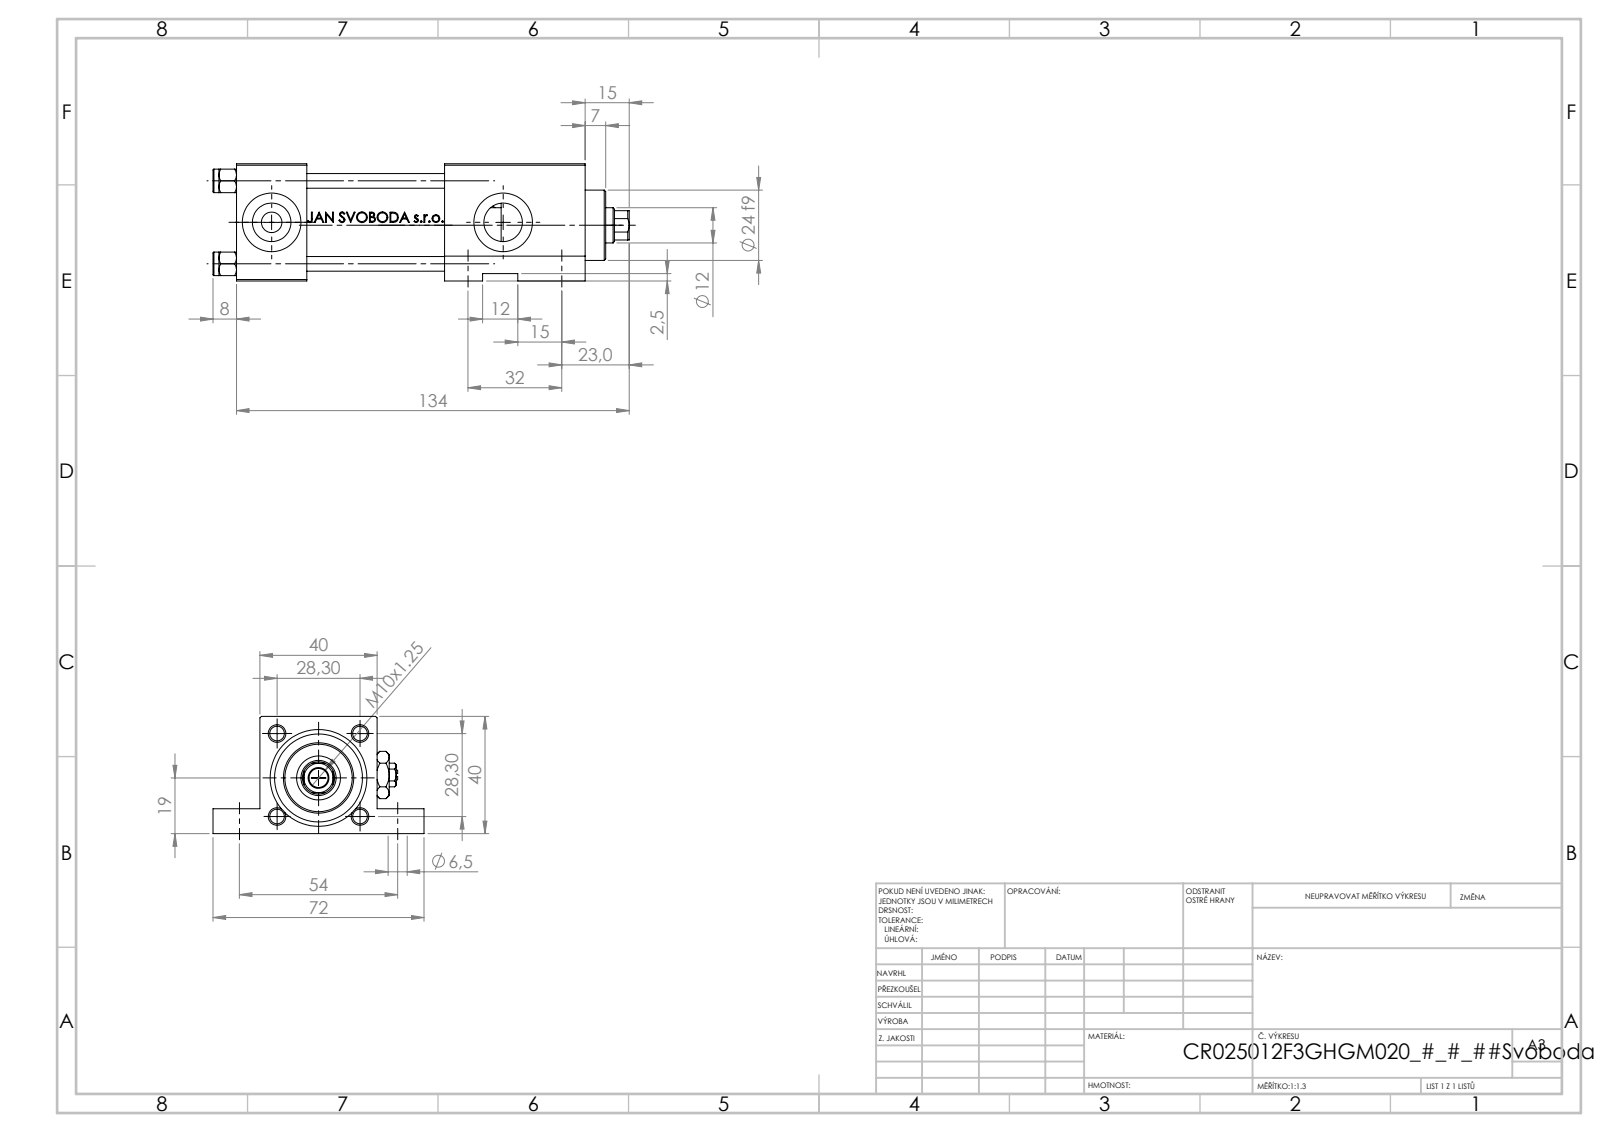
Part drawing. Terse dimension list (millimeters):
name: Zatka_pro_OIL_PORT; V215CR_F_Body; V215CR_VCP_F; V215_VC_A (+2 more)
written by: SolidWorks 2019 (CONFIG_CONTROL_DESIGN)
unit: mm
bodies: 13 solids, 1198 faces (482 planar, 134 cylindrical, 582 other)
size: 142 × 72 × 40
volume: 150 804 mm³; area: 60 276 mm²
holes: 5× ⌀6.5, 4× ⌀5, 4× ⌀20, 3× ⌀13.16, 2× ⌀7, 1× ⌀12, 1× ⌀13, 1× ⌀15, 1× ⌀25, 1× ⌀30
bosses: 4× ⌀8, 1× ⌀31, 1× ⌀24
rounds: 1× R5.5
face distances: 40, 24, 8.5, 31.5, 48, 47, 71, 119, 95, 39.8
hole spacings: 28.3, 19.32, 20.73, 32, 40.02, 54, 62.77, 7
